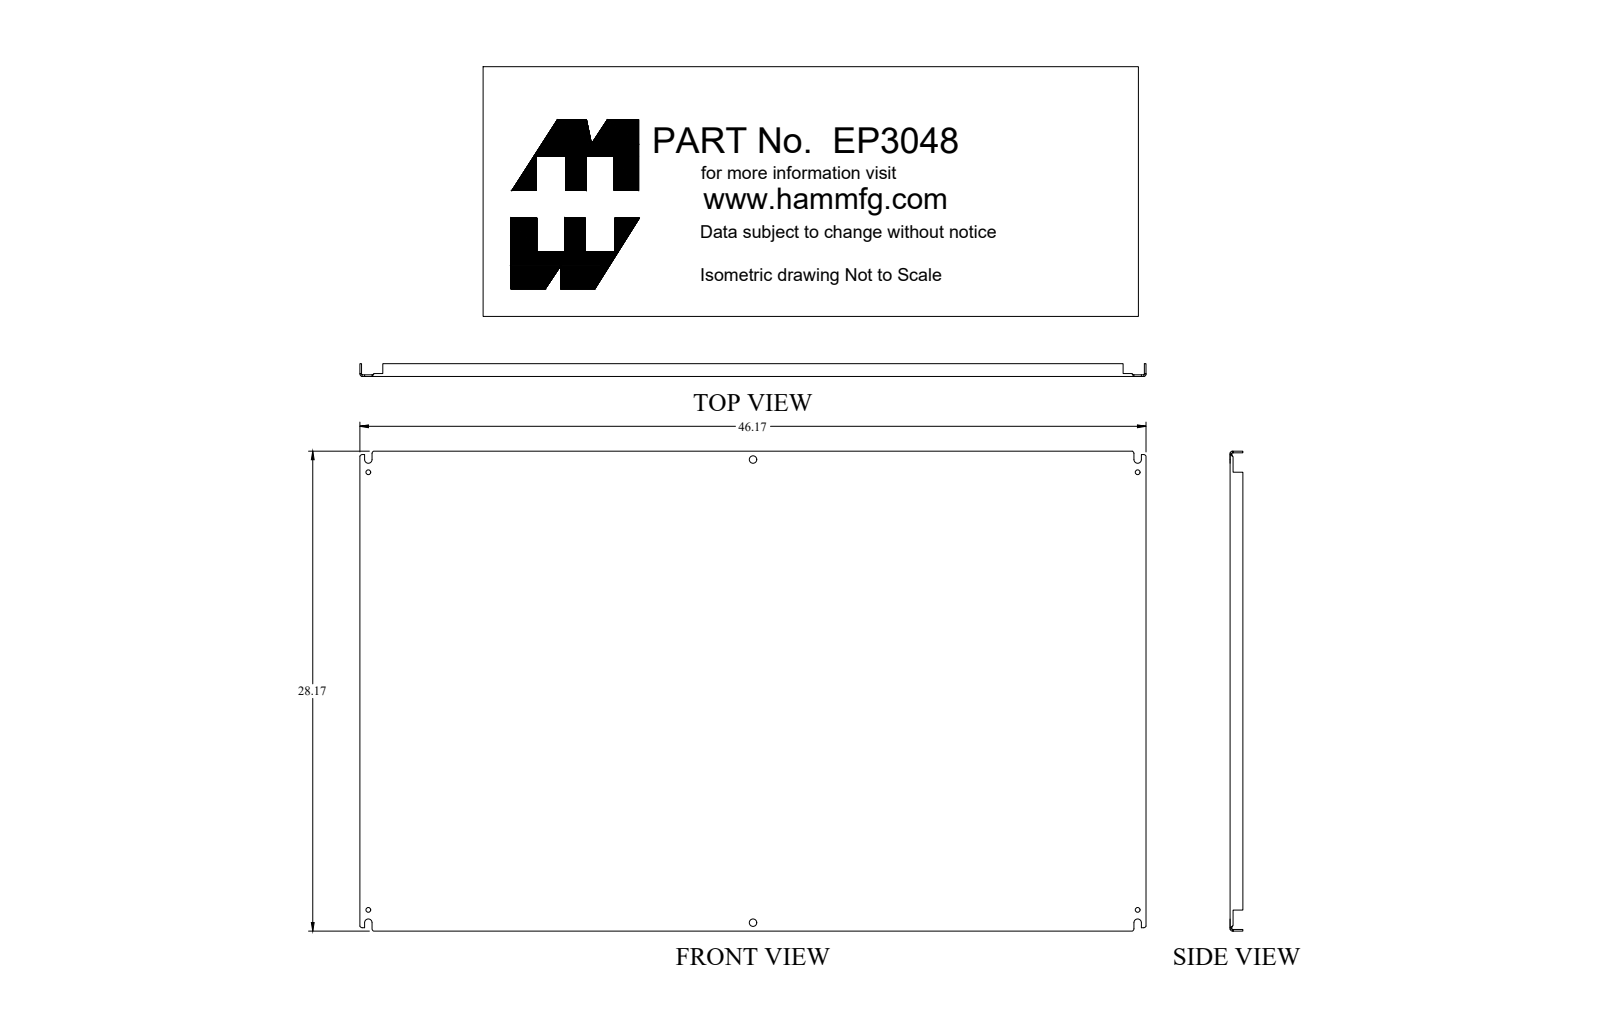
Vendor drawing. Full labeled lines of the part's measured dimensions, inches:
Part name (STEP PRODUCT): EP3048
STEP written by: SolidWorks 2018 (AUTOMOTIVE_DESIGN)
Units: inches
Bodies: 1 solid, 132 faces (74 planar, 42 cylindrical, 16 other)
Overall size (bounding box): 46.17 × 28.17 × 0.75
Volume: 131.4 in³ · Surface area: 2 783 in²
Round holes (diameter × count): ⌀0.281 ×4, ⌀0.437 ×2
Partial cylindrical surfaces — rounded edges, fillets, slot ends (radius × count): R0.048 ×4, R0.063 ×4, R0.143 ×4, R0.219 ×4
Main face-to-face distances: 0.095, 28.075, 46.075, 28.17, 27.98, 45.98, 46.17, 0.75, 0.655, 0.171
Hole centre spacings: 22.607, 34.778, 25.688, 45.188, 51.98, 27.188
